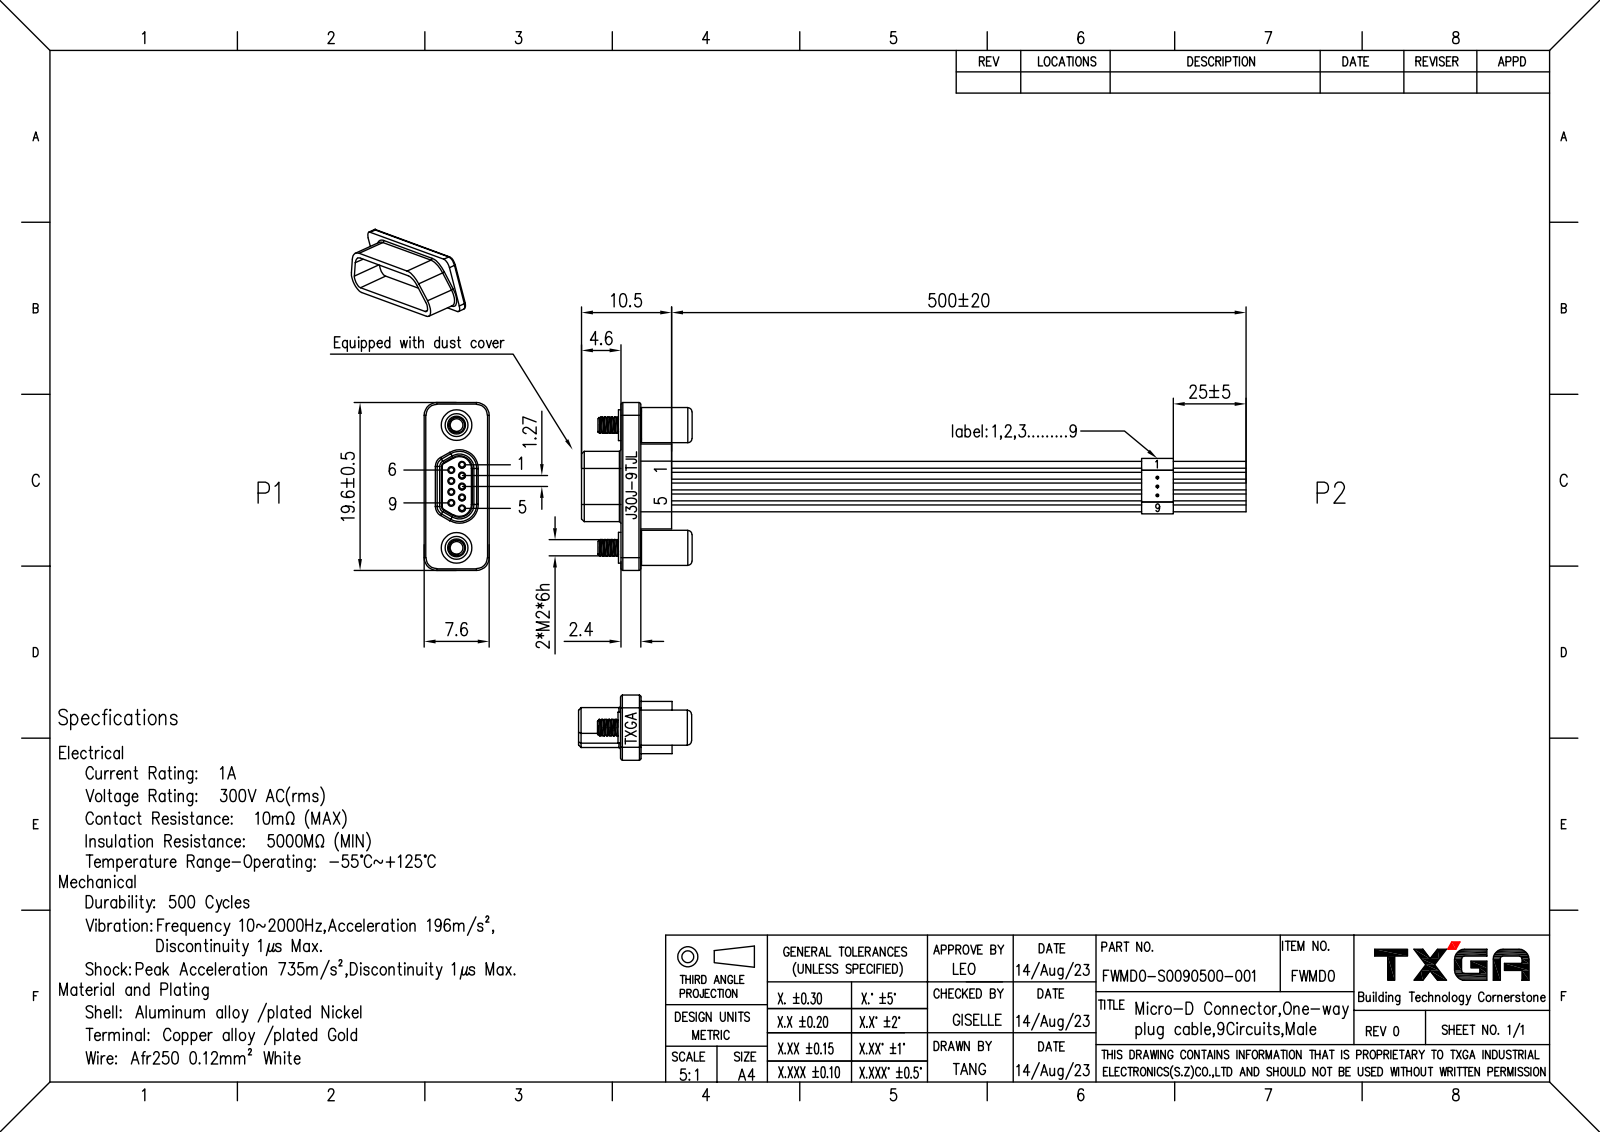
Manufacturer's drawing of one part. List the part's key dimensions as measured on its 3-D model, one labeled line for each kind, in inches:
Part name (STEP PRODUCT): LUOSISHELL; LUOS; MD09_ASM
STEP written by: PRO/ENGINEER BY PARAMETRIC TECHNOLOGY CORPORATION, 2010280 (CONFIG_CONTROL_DESIGN)
Units: inches
Bodies: 24 solids, 621 faces (301 planar, 222 cylindrical, 98 other)
Overall size (bounding box): 4.311 × 0.772 × 0.299
Volume: 0.076 in³ · Surface area: 6.217 in²
Round holes (diameter × count): ⌀0.031 ×3, ⌀0.083 ×2, ⌀0.11 ×2, ⌀0.126 ×2, ⌀0.138 ×2
Round bosses / shafts (diameter × count): ⌀0.031 ×9, ⌀0.024 ×9, ⌀0.161 ×2, ⌀0.142 ×2, ⌀0.128 ×2, ⌀0.075 ×2
Partial cylindrical surfaces — rounded edges, fillets, slot ends (radius × count): R0.008 ×28, R0.055 ×4, R0.059 ×4, R0.079 ×4, R0.016 ×2, R0.039 ×2, R0.063 ×2, R0.087 ×2
Main face-to-face distances: 0.193, 0.098, 0.024, 0.094, 0.039, 0.016, 0.122, 0.217, 0.283, 0.299
Hole centre spacings: 0.05, 0.233, 0.283, 0.332, 0.1, 0.563
